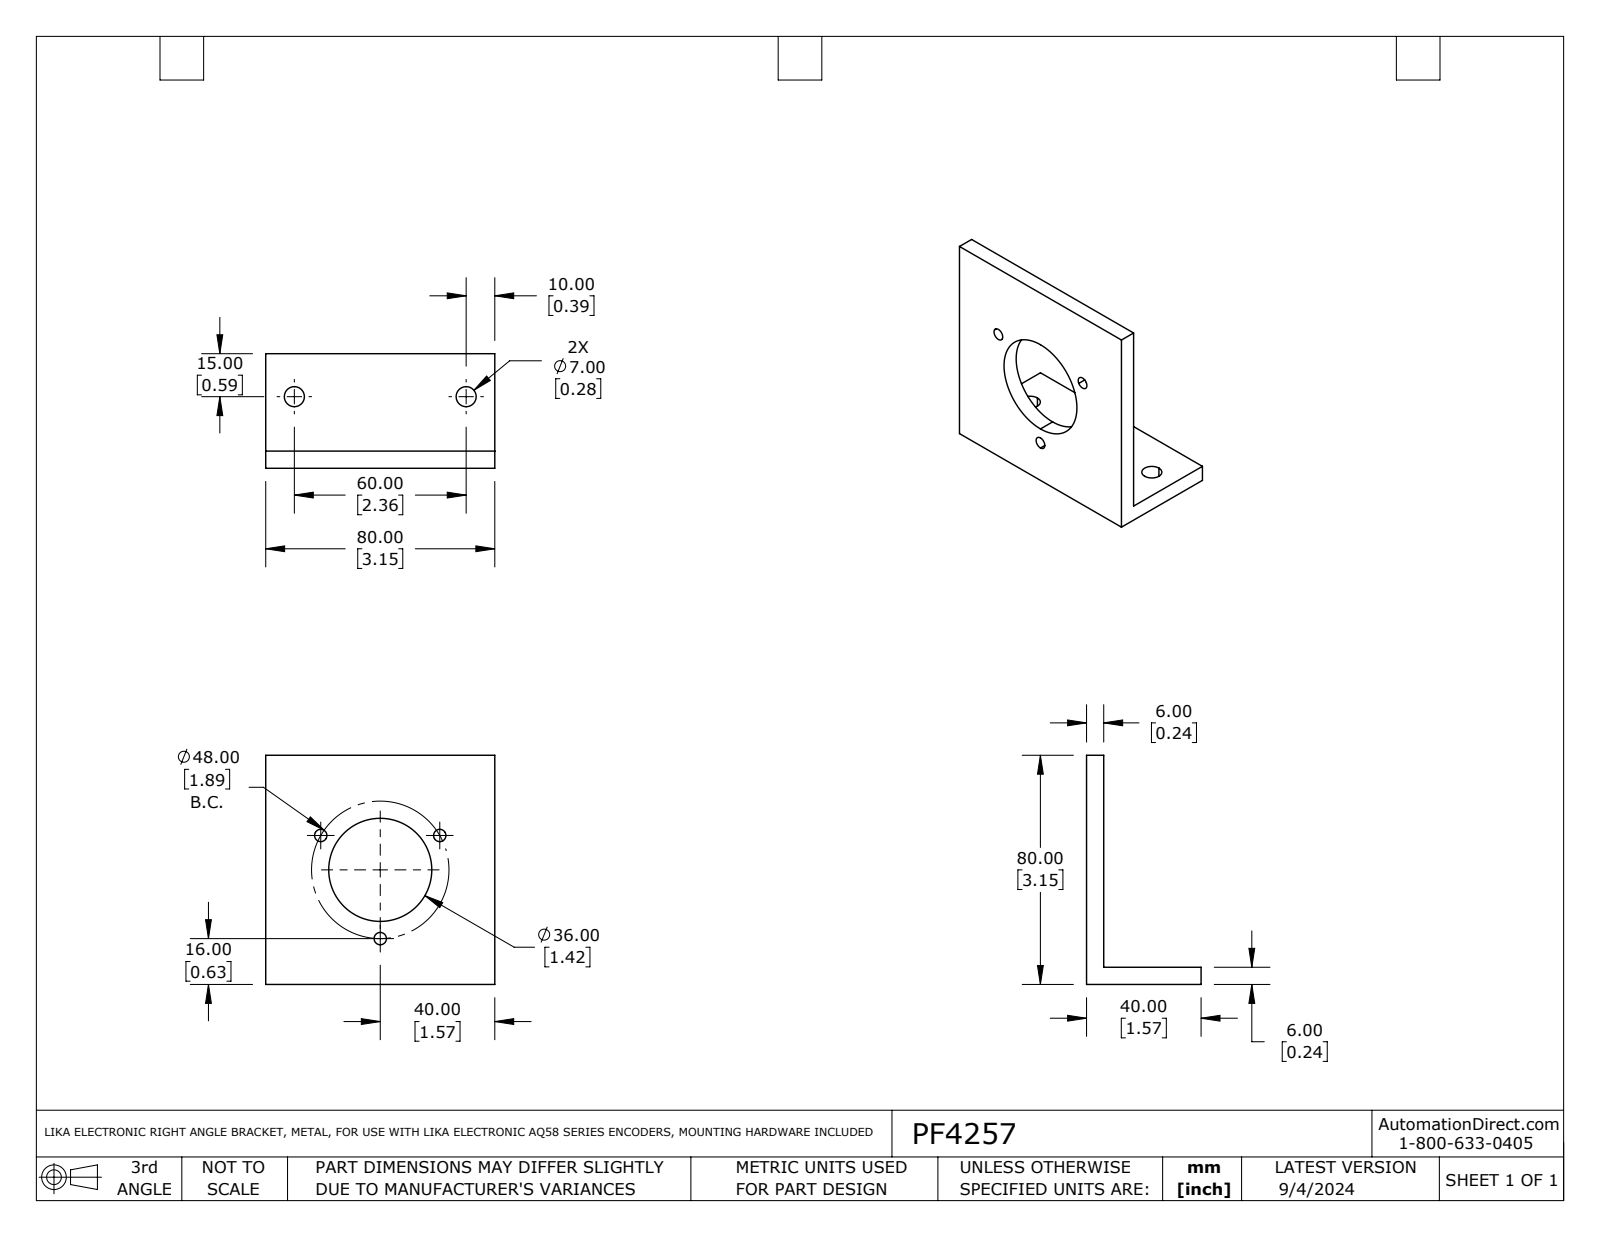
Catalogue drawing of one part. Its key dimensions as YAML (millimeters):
part_name: "PF4257"
step_written_by: "SolidWorks 2021 (AUTOMOTIVE_DESIGN)"
units: millimeters
bodies: {solids: 1, faces: 26, planar: 8, cylindrical: 18, other: 0}
overall_size: [80, 80, 40]
volume: 47880
surface_area: 19480
round_holes:
  - {diameter: 4.3, count: 3}
  - {diameter: 7, count: 2}
  - {diameter: 36, count: 1}
face_to_face_distances: [6, 80, 40, 34, 74]
hole_center_spacings: [24, 41.6, 41.6, 60]
